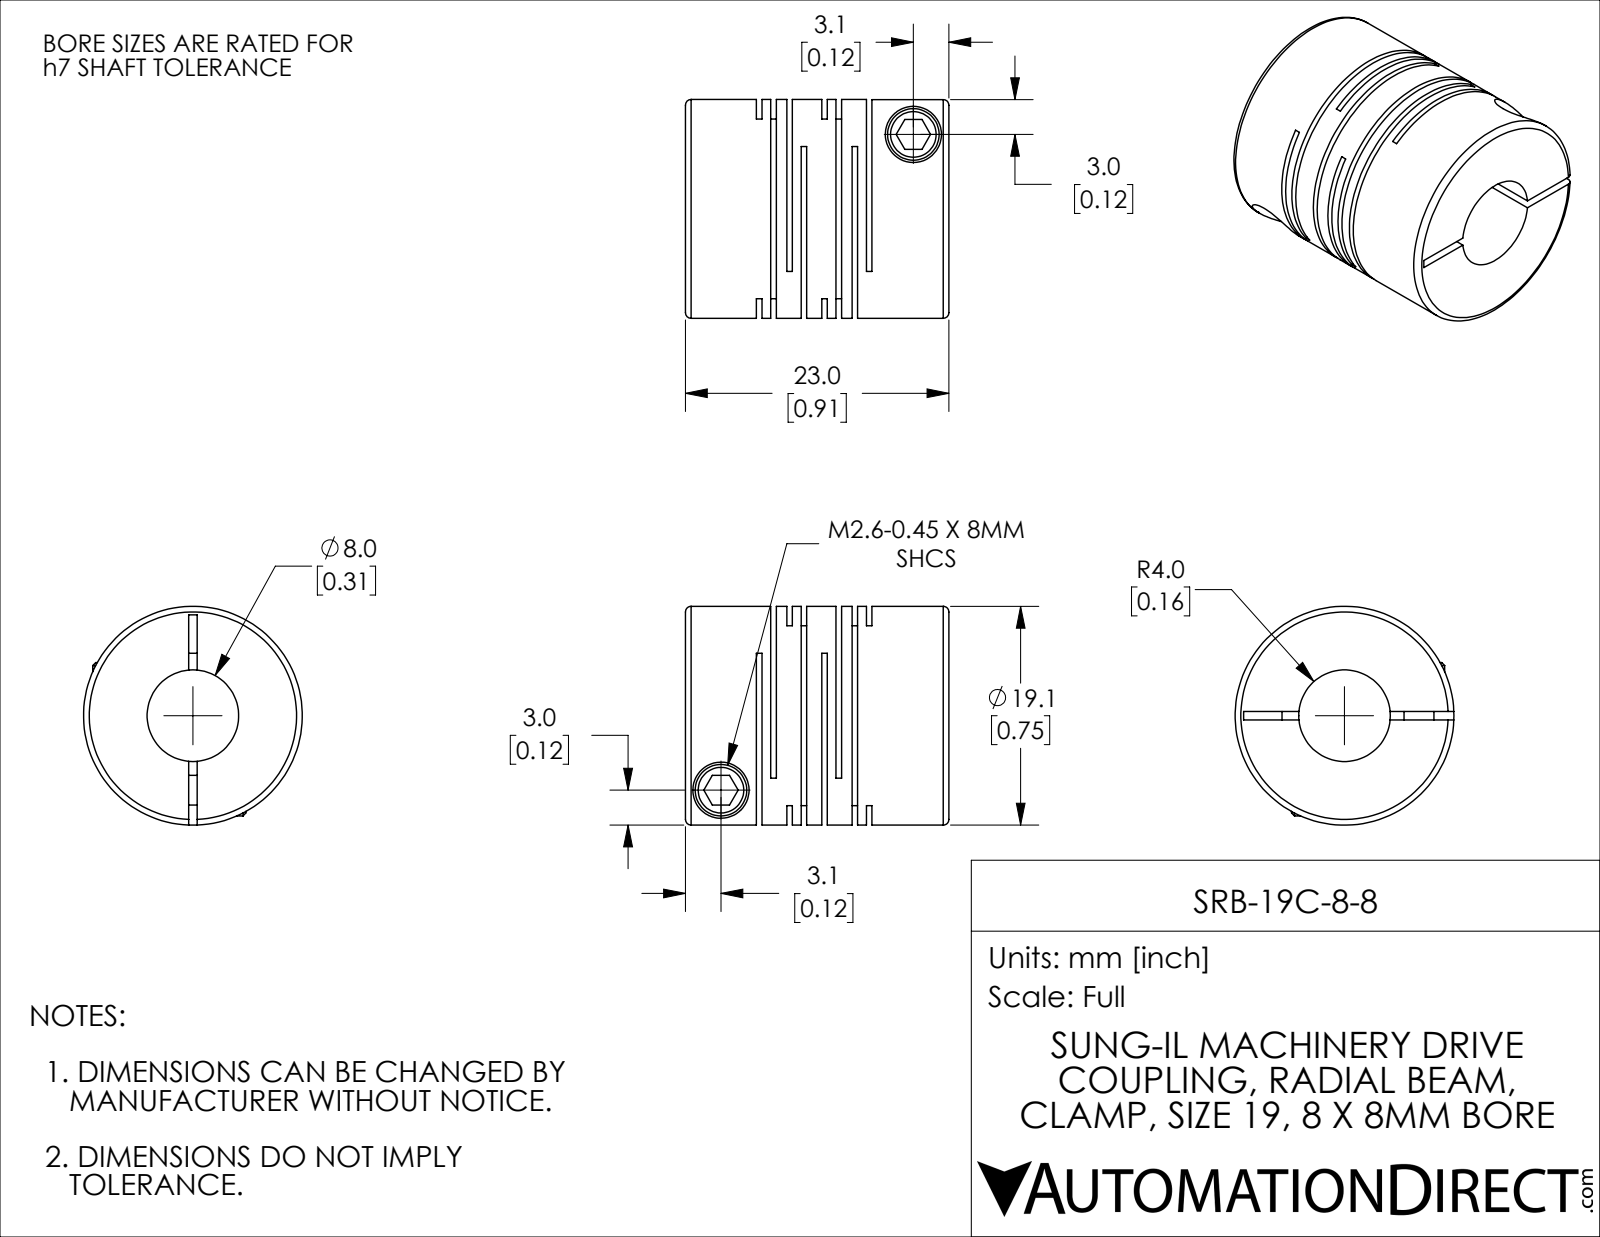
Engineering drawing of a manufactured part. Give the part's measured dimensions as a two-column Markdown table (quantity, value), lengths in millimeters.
| quantity | value |
| --- | --- |
| part name | SRB-19C-8-8 |
| STEP written by | SolidWorks 2021 (CONFIG_CONTROL_DESIGN) |
| units | millimeters |
| bodies | 1 solid, 114 faces (60 planar, 42 cylindrical, 12 other) |
| overall size | 23 × 19.1 × 19.1 |
| volume | 4 479 mm³ |
| surface area | 5 694 mm² |
| round holes (diameter × count) | 2.6 × 2, 4.9 × 2, 8 × 1 |
| round bosses / shafts (diameter × count) | 4.5 × 2, 19.1 × 1 |
| main face-to-face distances | 1.25, 5.7, 0.48, 2.65, 2.17, 3.05, 5.22, 4.45, 0.77, 1.4 |
